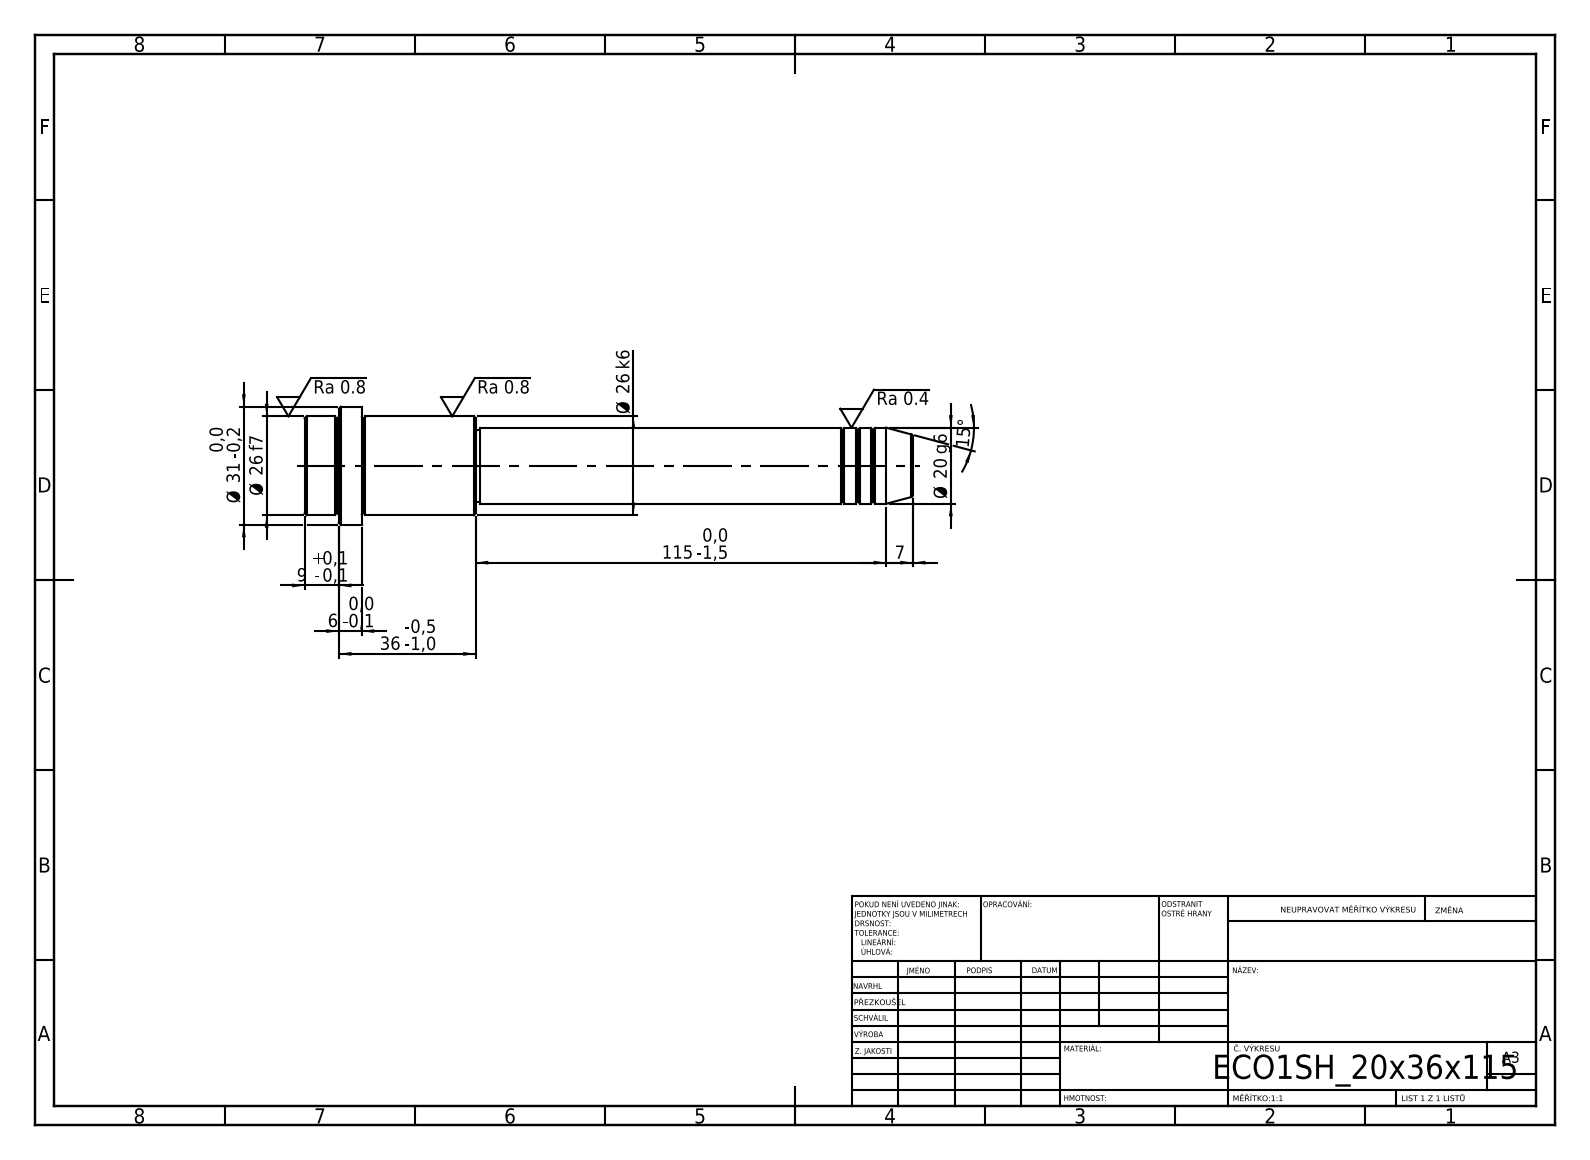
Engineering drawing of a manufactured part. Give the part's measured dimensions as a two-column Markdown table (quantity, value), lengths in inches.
| quantity | value |
| --- | --- |
| STEP written by | SolidWorks 2019 (CONFIG_CONTROL_DESIGN) |
| units | inches |
| bodies | 1 solid, 52 faces (6 planar, 16 cylindrical, 30 other) |
| overall size | 6.299 × 1.22 × 1.22 |
| volume | 3.709 in³ |
| surface area | 19.42 in² |
| round bosses / shafts (diameter × count) | 1.22 × 1, 1.024 × 1, 0.787 × 1, 0.748 × 1 |
| main face-to-face distances | 0.591, 1.181, 1.772, 4.528, 5.709, 6.299, 5.945, 1.417, 0.236, 0.354 |
